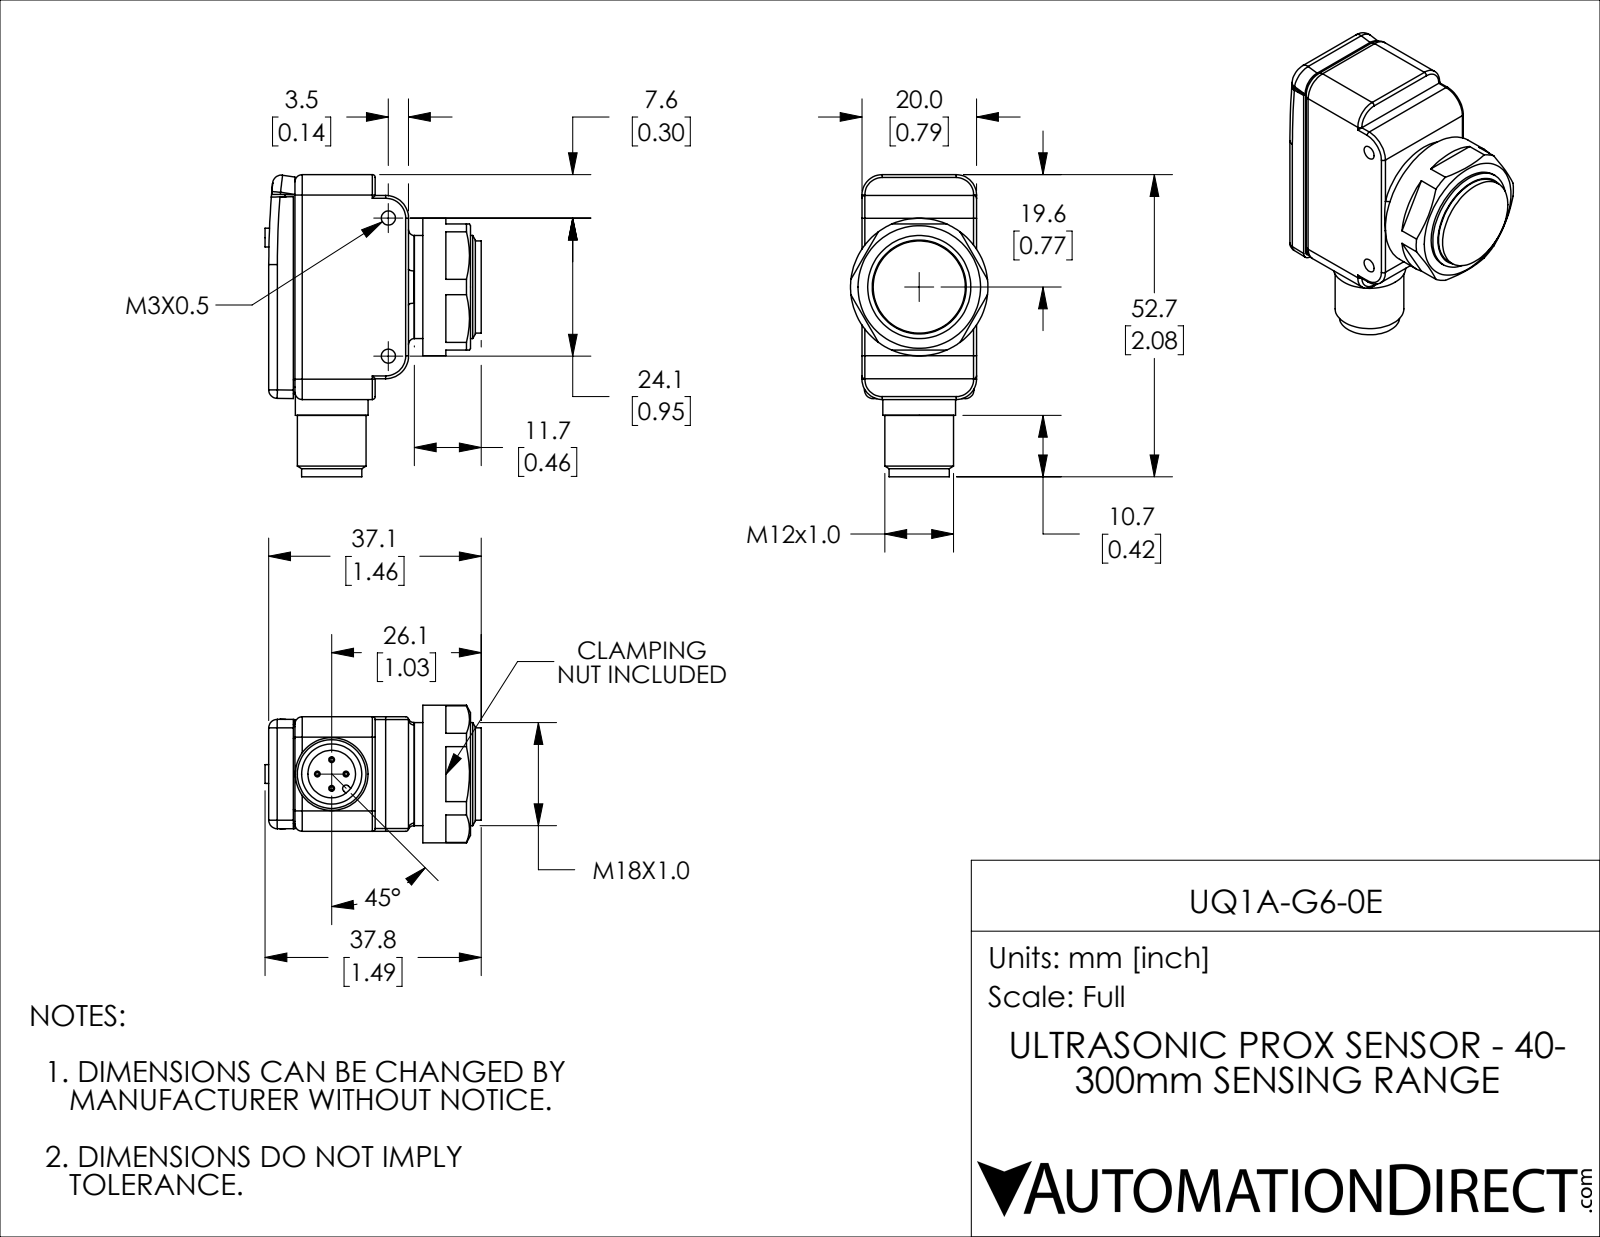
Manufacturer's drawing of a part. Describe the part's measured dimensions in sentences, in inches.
The part is named "UQ1A-G6-0E". Its 3-D file was written by "SolidWorks 2018 (AUTOMOTIVE_DESIGN)". It is 7 solids with 203 faces: 81 planar, 72 cylindrical and 50 other. Overall it measures 2.076 by 1.486 by 0.945 inches. Its volume is 1.389 cubic inches and its surface area 17.13 square inches. Round holes: 2 of diameter 0.097, 1 of diameter 0.13, 1 of diameter 0.327. Round bosses or shafts: 4 of diameter 0.039, 1 of diameter 0.945, 1 of diameter 0.709, 1 of diameter 0.634, 1 of diameter 0.5, 1 of diameter 0.472, 1 of diameter 0.413. Partial cylindrical surfaces (rounded edges, fillets, slot ends): 10 of radius 0.02, 6 of radius 0.059, 4 of radius 0.049, 4 of radius 0.14, 2 of radius 0.118, 2 of radius 0.157, 2 of radius 5.906, 1 of radius 0.024. The main face-to-face distances are 0.091, 0.787, 0.911, 0.82, 0.09, 0.181, 1.001, 0.459, 1.46, 1.37. The hole center spacings are 0.949.
